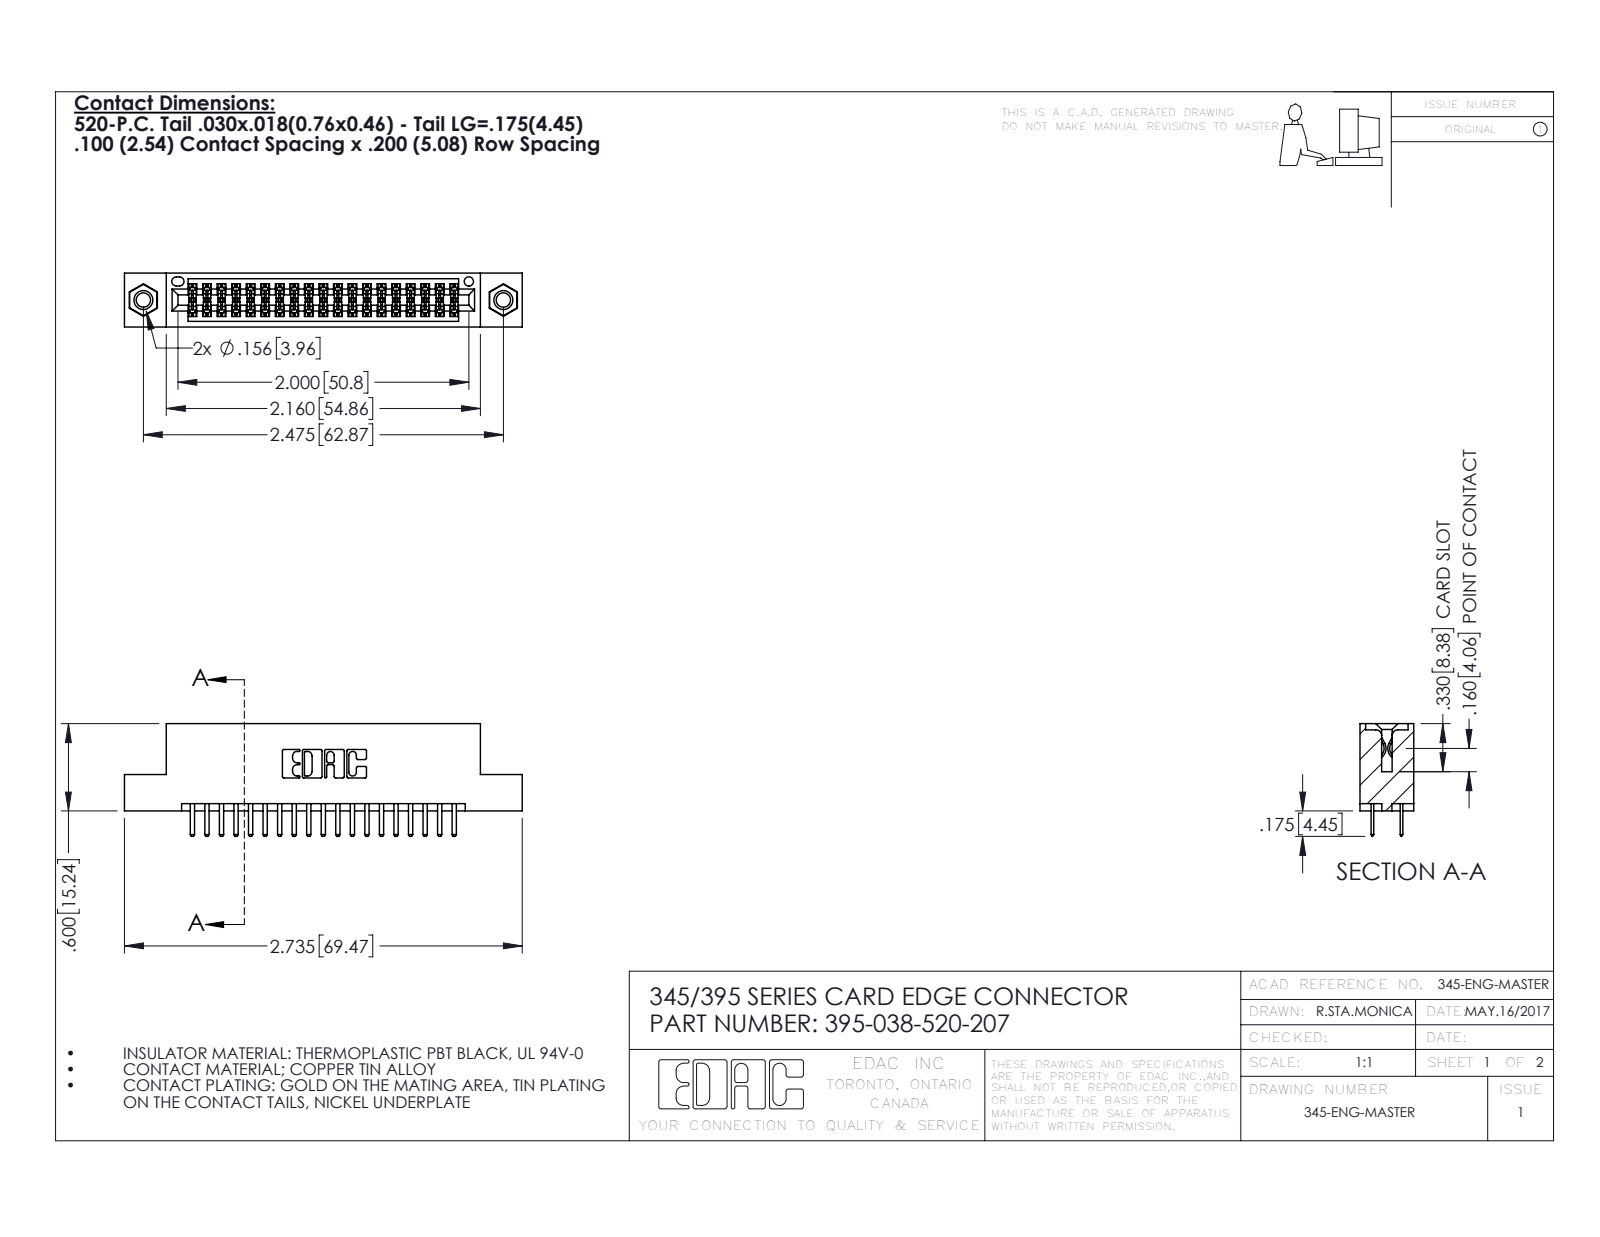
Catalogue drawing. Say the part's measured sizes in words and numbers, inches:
The part is named "345 Part_Flush Mounting Lugs - 0.156 Dia-TI; 345-250-001_345-250-005-103; 395-038-520-207; 345-292-001_345-293-120". Its 3-D file was written by "SolidWorks 2016 (CONFIG_CONTROL_DESIGN)". It is 41 solids with 2238 faces: 1442 planar, 780 cylindrical and 16 other. Overall it measures 2.735 by 0.775 by 0.37 inches. Its volume is 0.397 cubic inches and its surface area 14.2 square inches. Round holes: 2 of diameter 0.098, 2 of diameter 0.125, 2 of diameter 0.156, 1 of diameter 0.064. Round bosses or shafts: 2 of diameter 0.155. Partial cylindrical surfaces (rounded edges, fillets, slot ends): 57 of radius 0.006, 42 of radius 0.01, 22 of radius 0.01, 6 of radius 0.007, 6 of radius 0.031, 3 of radius 0.026, 2 of radius 0.014, 2 of radius 0.019. The main face-to-face distances are 0.2, 0.072, 0.298, 0.37, 0.098, 0.272, 0.025, 0.225, 0.022, 0.072. The hole center spacings are 0.27, 2.241, 2.475.
